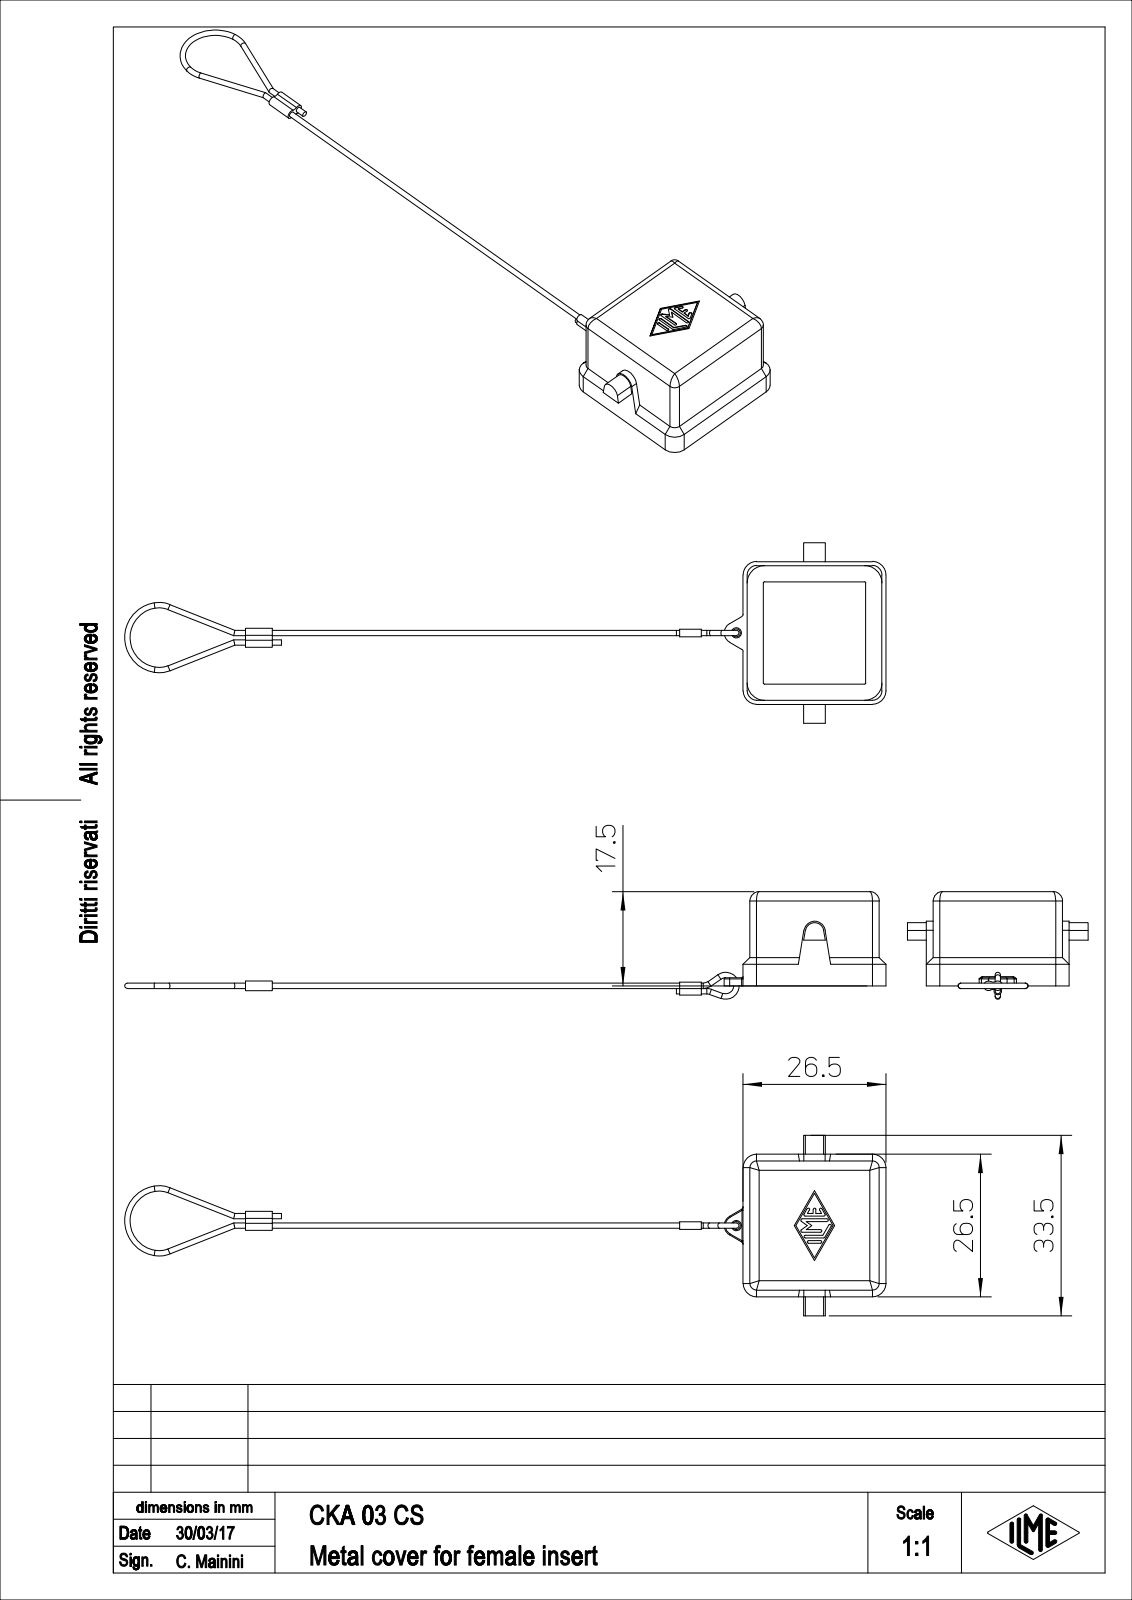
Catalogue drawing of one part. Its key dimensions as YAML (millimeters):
part_name: "CKA_03_CS"
step_written_by: "PTC Creo Elements/Direct Modeling 19.0E 27-Jun-2016 (C) Parametric Technology GmbH (AUTOMOTIVE_DESIGN)"
units: millimeters
bodies: {solids: 1, faces: 205, planar: 93, cylindrical: 82, other: 30}
overall_size: [141.21, 33.5, 20]
volume: 3901
surface_area: 5182
round_holes:
  - {diameter: 1.5, count: 1}
round_bosses_or_shafts:
  - {diameter: 1, count: 7}
partial_cylinders:
  - {radius: 0.25, count: 14}
  - {radius: 1.75, count: 12}
  - {radius: 0.2, count: 7}
  - {radius: 1.25, count: 4}
  - {radius: 2.5, count: 4}
  - {radius: 3.2, count: 4}
  - {radius: 0.5, count: 2}
  - {radius: 0.7, count: 2}
face_to_face_distances: [1.25, 22.75, 24, 2.5, 21.5, 2, 25.25, 20.25, 3.75, 16]
